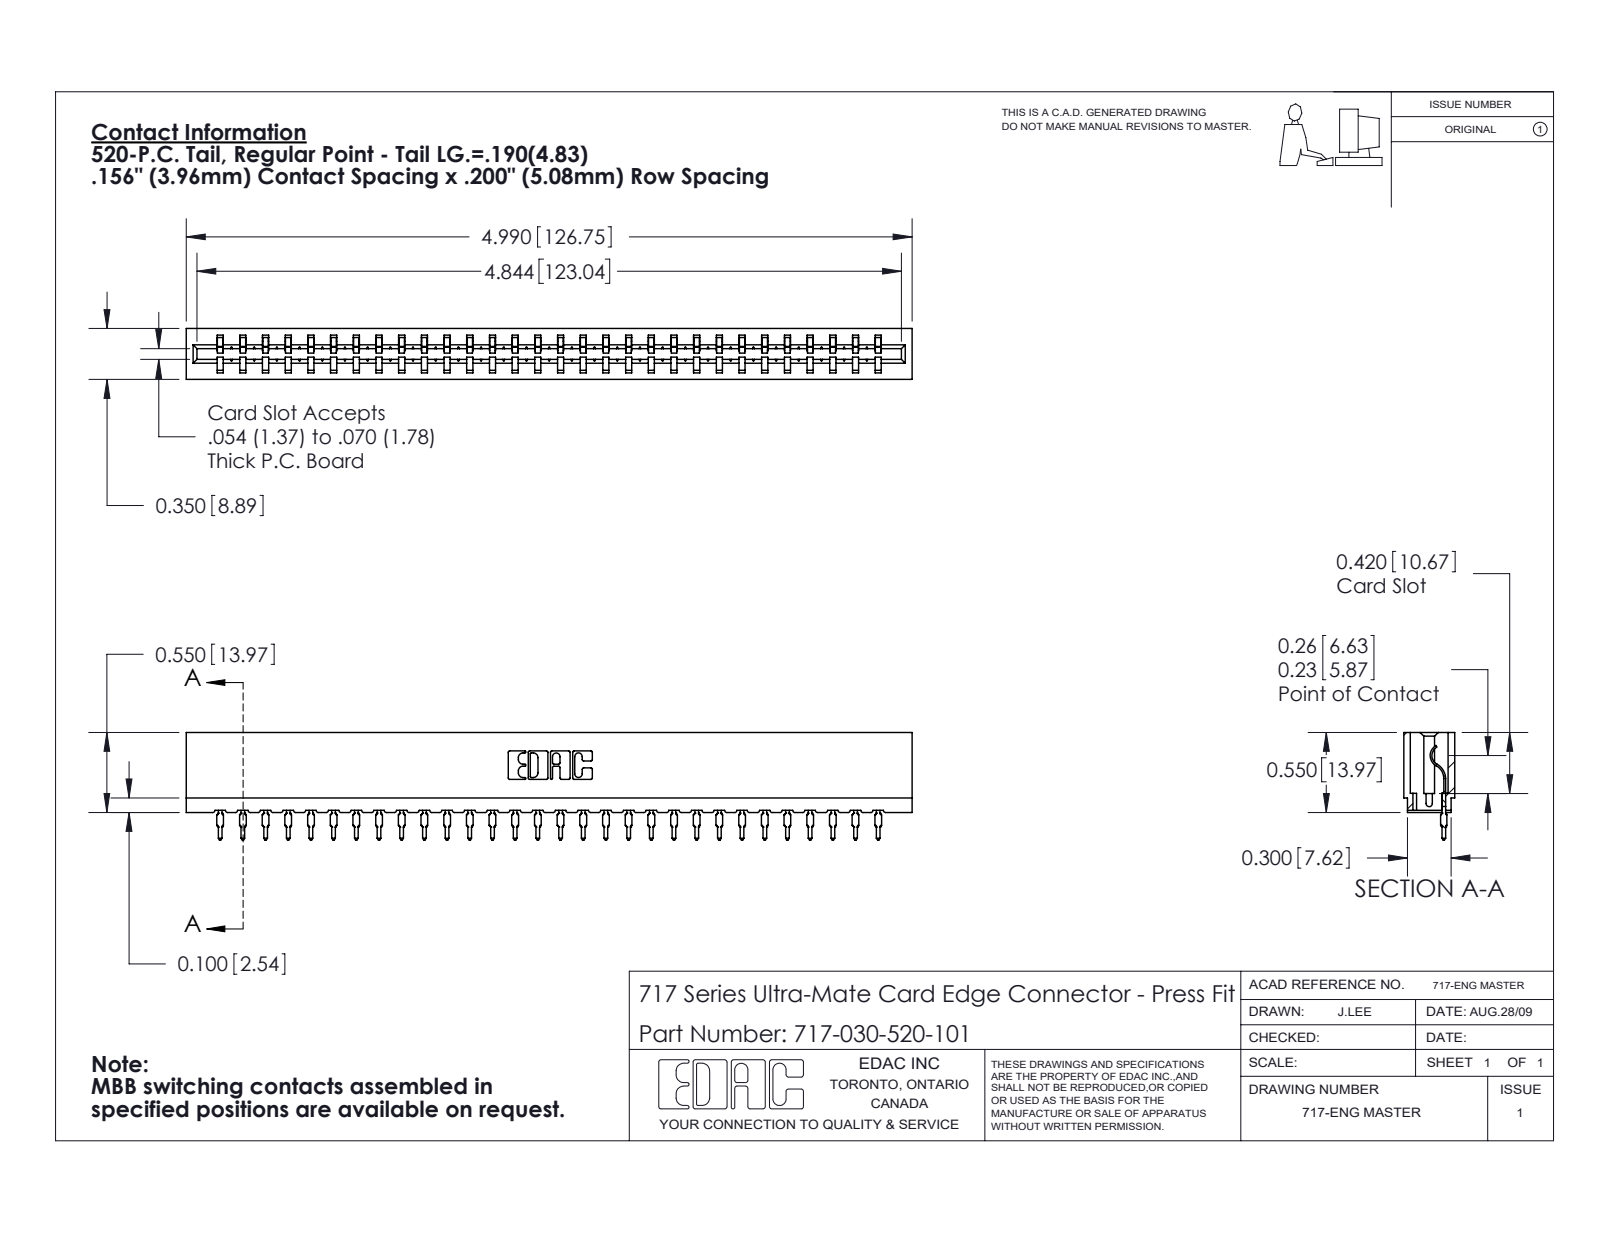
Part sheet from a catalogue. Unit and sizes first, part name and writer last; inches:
Units: inches
Overall size (bounding box): 4.99 × 0.739 × 0.35
Partial cylindrical surfaces — rounded edges, fillets, slot ends (radius × count): R0.015 ×60, R0.021 ×60, R0.01 ×22, R0.007 ×6, R0.031 ×6, R0.005 ×4, R0.011 ×4, R0.026 ×3
Main face-to-face distances: 0.212, 0.138, 0.35, 0.074, 0.156, 0.045, 0.305, 0.093, 0.167, 0.025
Volume: 0.654 in³ · Surface area: 22.8 in²
Bodies: 31 solids, 3484 faces (2094 planar, 610 cylindrical, 780 other)
Part name (STEP PRODUCT): 717 Part_Insulator Option - 06; 717-030-520-101; 745-292-001_520
STEP written by: SolidWorks 2020 (CONFIG_CONTROL_DESIGN)
